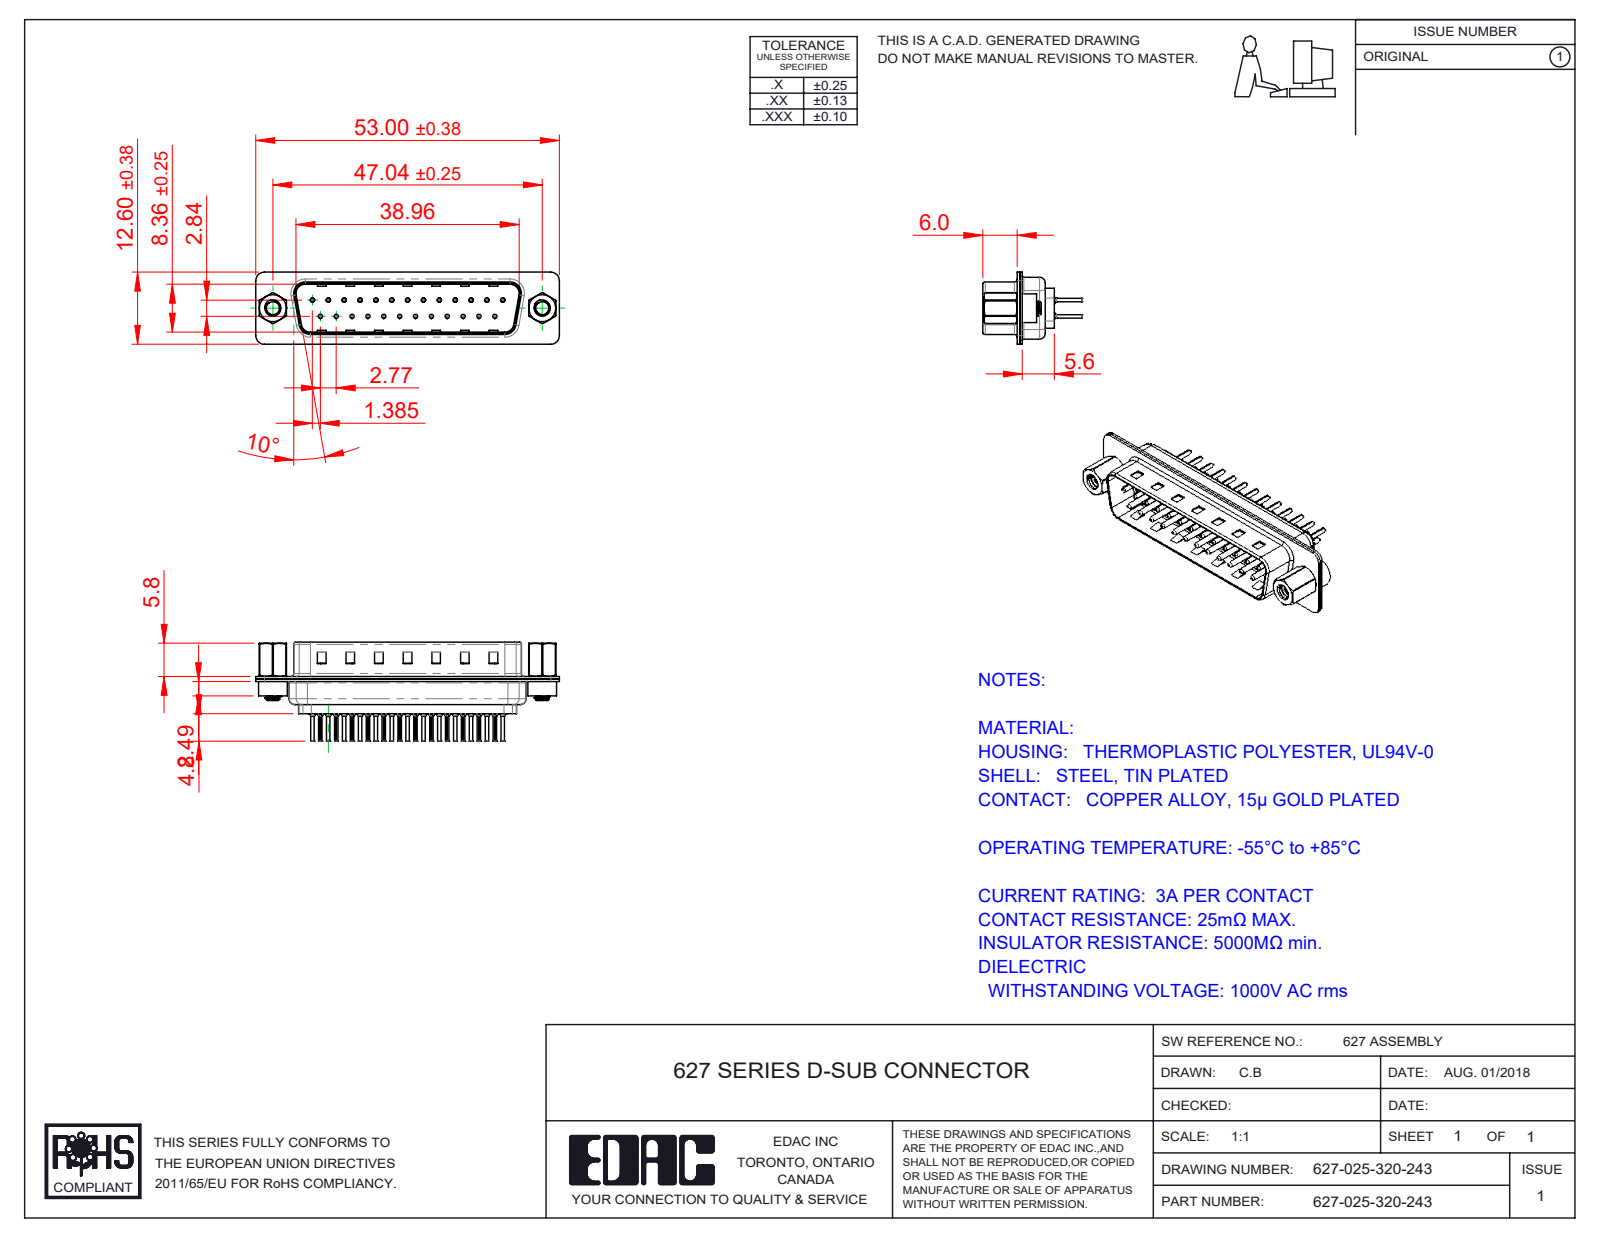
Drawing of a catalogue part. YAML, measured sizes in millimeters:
part_name: "627 Contact Row 2_20L; 627 Shell Front_25 Contacts; 627 4-40 Hex Standoff; 627 4-40 Threaded Rivet (+4 more)"
step_written_by: "SolidWorks 2020 (CONFIG_CONTROL_DESIGN)"
units: millimeters
bodies: {solids: 32, faces: 2948, planar: 793, cylindrical: 1132, other: 1023}
overall_size: [53, 17.3, 12.6]
volume: 2890
surface_area: 8277
round_holes:
  - {diameter: 0.2, count: 25}
  - {diameter: 0.35, count: 25}
  - {diameter: 1.1, count: 25}
  - {diameter: 1.6, count: 25}
  - {diameter: 2.26, count: 2}
  - {diameter: 2.29, count: 2}
  - {diameter: 4, count: 2}
  - {diameter: 4.8, count: 2}
round_bosses_or_shafts:
  - {diameter: 2, count: 25}
  - {diameter: 1.5, count: 25}
  - {diameter: 0.75, count: 25}
  - {diameter: 0.6, count: 25}
  - {diameter: 5, count: 2}
  - {diameter: 4.9, count: 2}
  - {diameter: 2.79, count: 2}
partial_cylinders:
  - {radius: 0.1, count: 50}
  - {radius: 1.5, count: 16}
  - {radius: 2, count: 12}
  - {radius: 0.5, count: 8}
  - {radius: 1.6, count: 8}
  - {radius: 0.25, count: 4}
  - {radius: 0.6, count: 4}
  - {radius: 0.65, count: 4}
face_to_face_distances: [0.4, 0.45, 0.82, 9.58, 8.76, 0.9, 1.5, 1.4, 6.5, 6.05]
hole_center_spacings: [3.16, 8.31, 2.77, 5.54, 11.08, 16.62, 5.03, 5.04]
